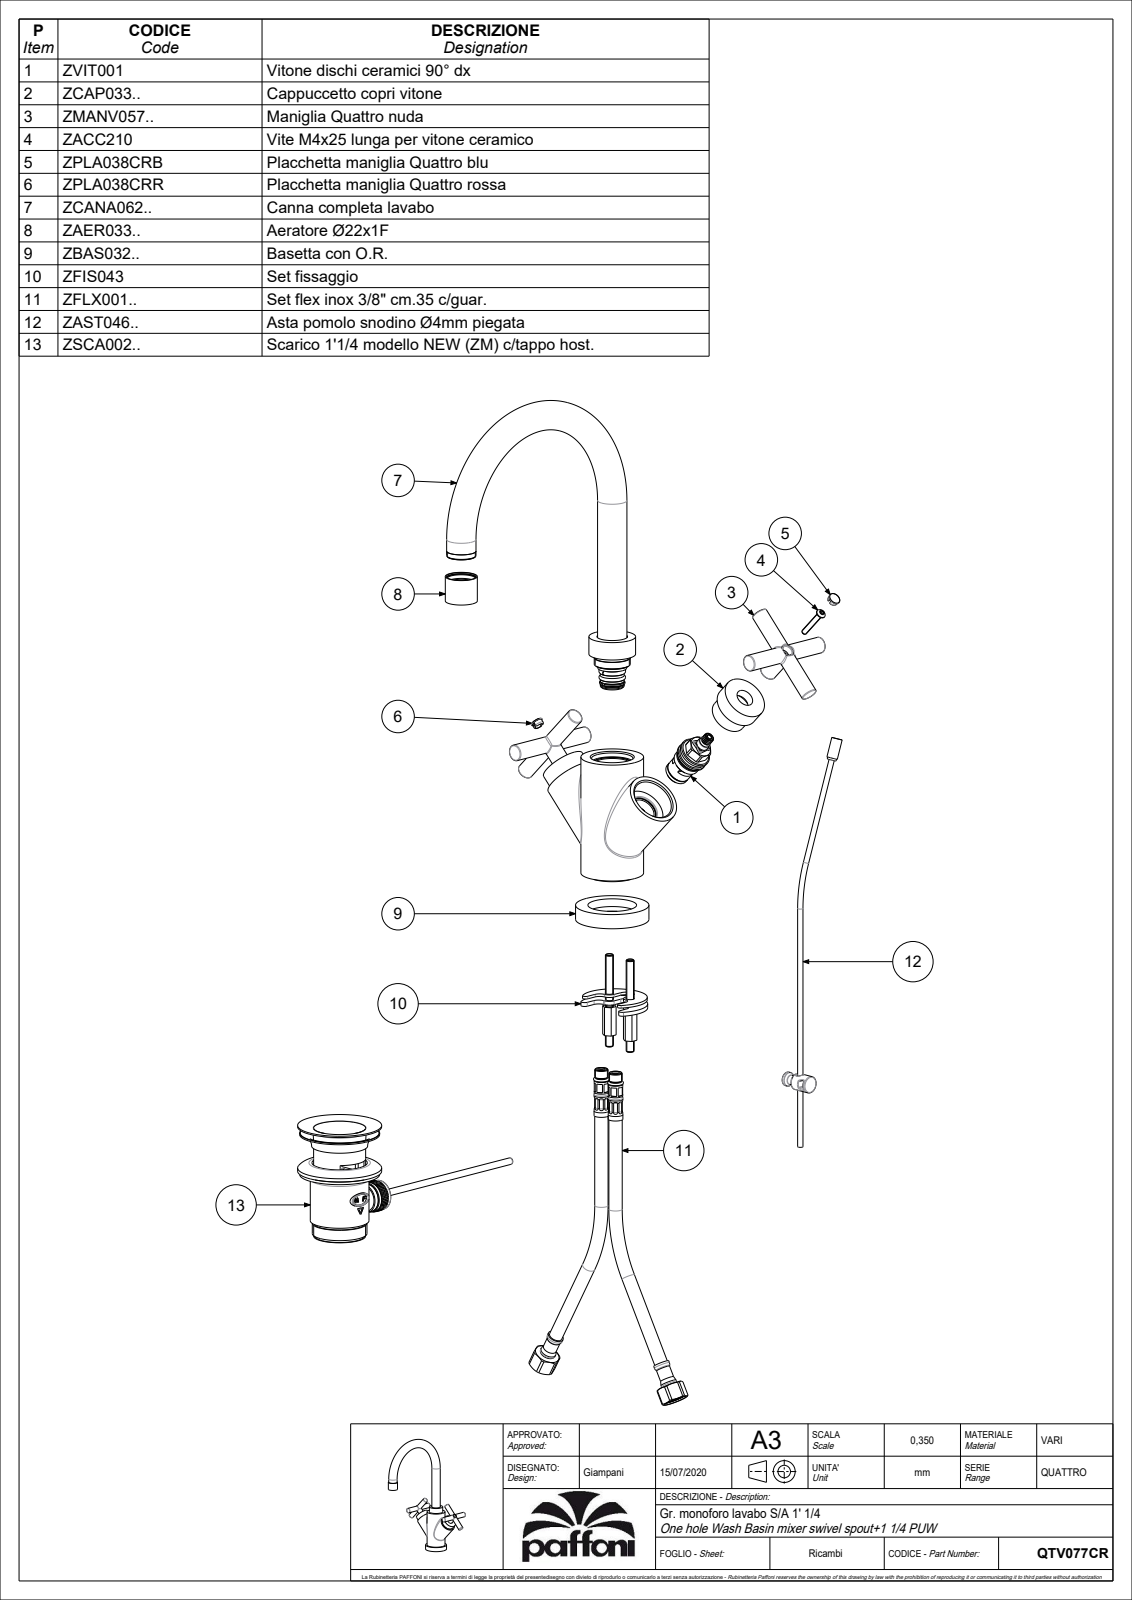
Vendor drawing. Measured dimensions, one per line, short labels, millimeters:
name: QTV077CR
written by: CREO PARAMETRIC BY PTC INC, 2020044 (CONFIG_CONTROL_DESIGN)
unit: mm
bodies: 8 solids, 2426 faces (1876 planar, 308 cylindrical, 242 other)
size: 311.2 × 210.03 × 192.61
volume: 313 194 mm³; area: 134 673 mm²
holes: 4× ⌀7, 4× ⌀9, 4× ⌀19, 3× ⌀8, 2× ⌀3.3, 2× ⌀4.5, 2× ⌀4.6, 2× ⌀8.8, 2× ⌀9.5, 2× ⌀10.3, 2× ⌀11, 2× ⌀13.5
bosses: 4× ⌀12, 3× ⌀24, 2× ⌀40, 2× ⌀34, 2× ⌀28, 2× ⌀22, 2× ⌀21.4, 2× ⌀18.6
rounds: 34× R0.1, 4× R0.5, 4× R1, 2× R3, 2× R9.3, 2× R9.4
face distances: 12, 13.5, 5, 4, 11, 92, 9, 2, 1, 1.5
hole spacings: 8.5, 15.88, 156.18, 10, 15, 160, 170
